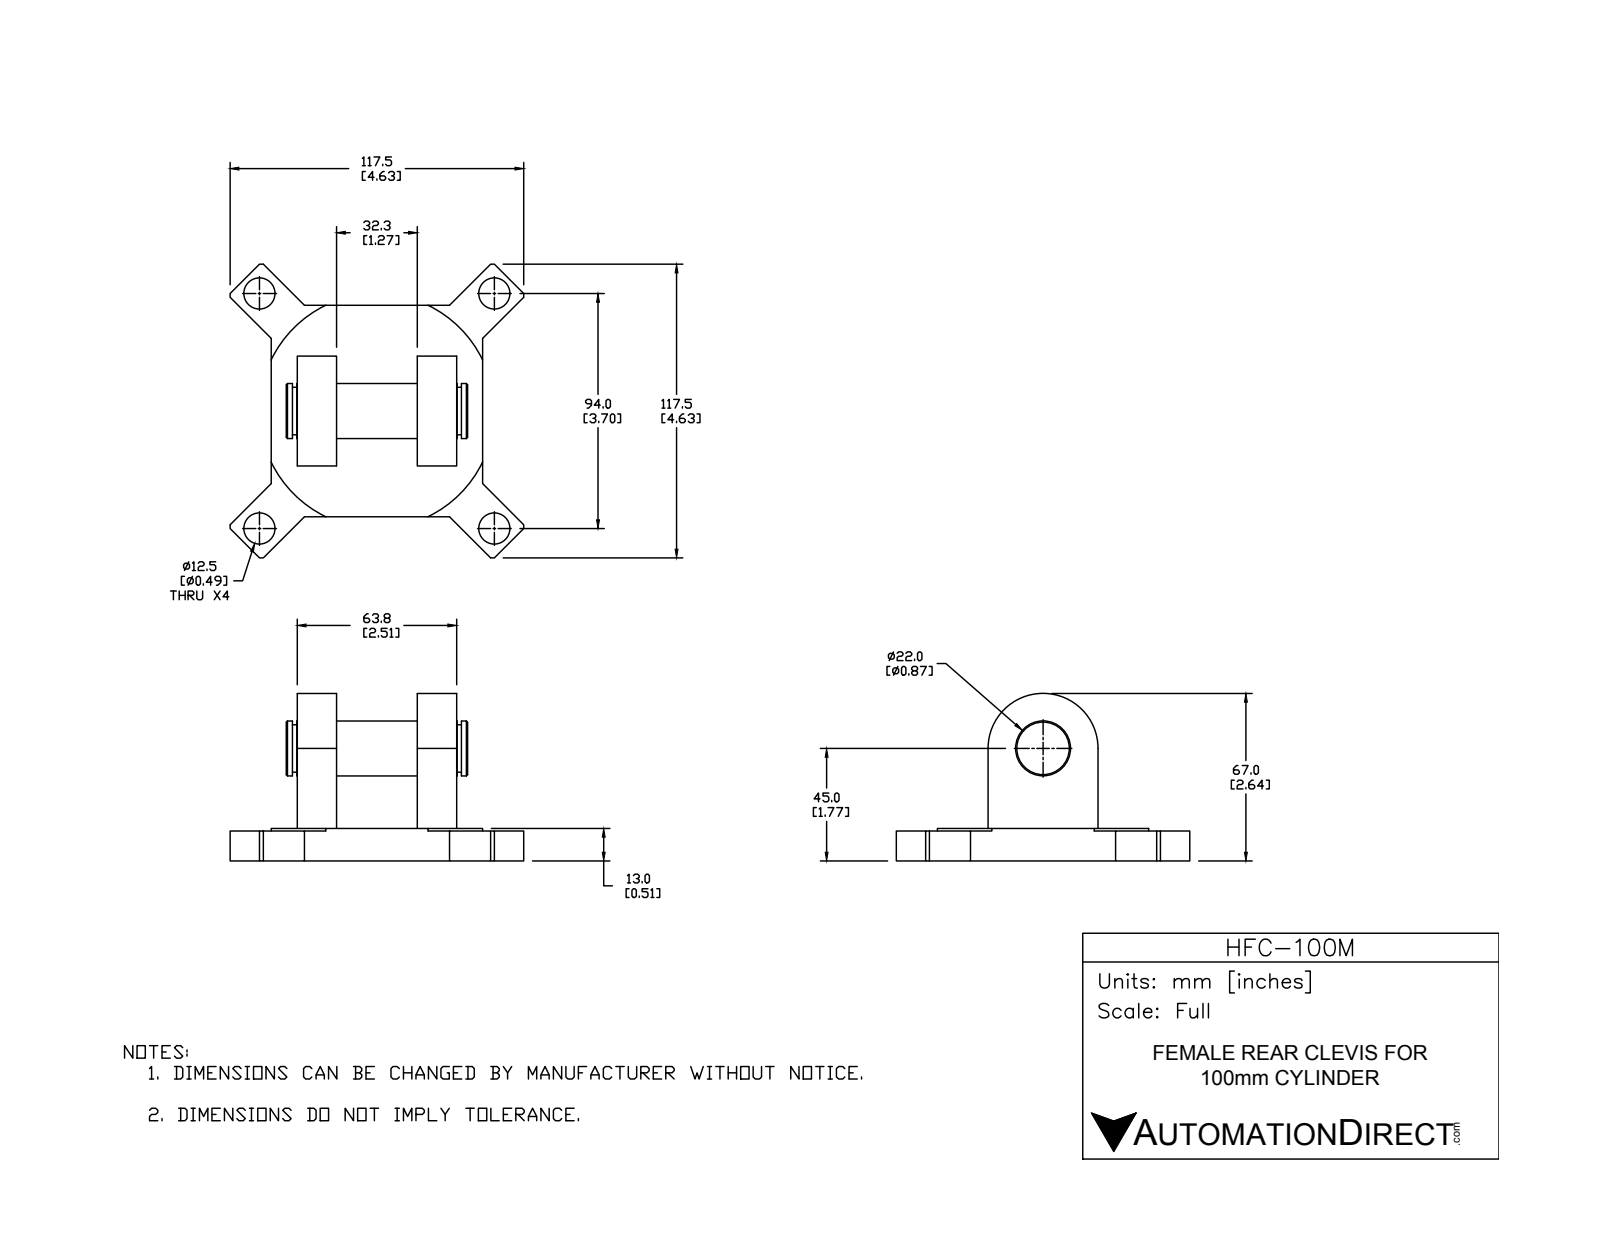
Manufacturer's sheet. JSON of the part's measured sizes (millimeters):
{"part_name": "HFC-100M", "step_written_by": "SolidWorks 2015 (CONFIG_CONTROL_DESIGN)", "units": "millimeters", "bodies": {"solids": 2, "faces": 76, "planar": 44, "cylindrical": 28, "other": 4}, "overall_size": [117.5, 117.5, 67], "volume_mm3": 187621, "surface_area_mm2": 42637, "round_holes": [[12.5, 4]], "round_bosses_or_shafts": [[22, 1], [19, 1]], "partial_cylinders_radius": [[22, 1], [47, 1]], "face_to_face_distances": [13, 48.05, 15.75, 32.3, 63.8, 12, 1, 10.4, 26.15, 58.45], "hole_center_spacings": [94, 132.94]}
